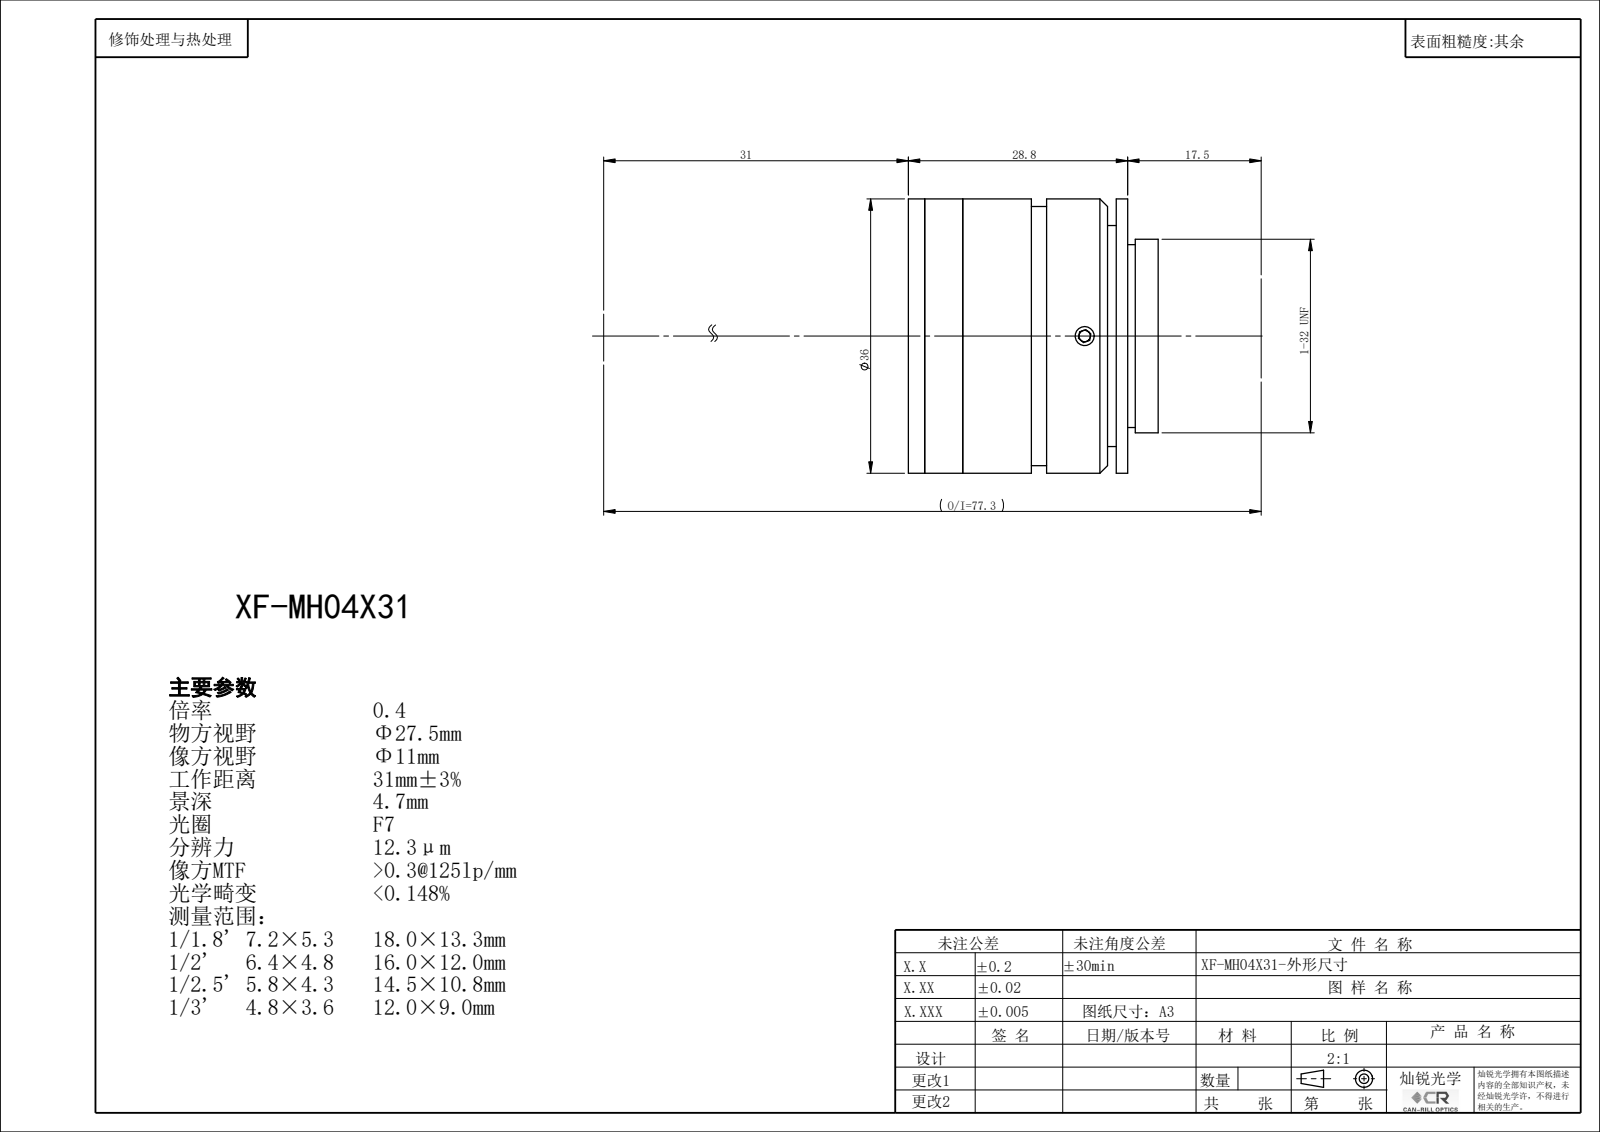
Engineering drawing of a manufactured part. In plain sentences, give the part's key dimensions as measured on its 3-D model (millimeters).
The part is named "XF-MH04X31". Its 3-D file was written by "SolidWorks 2022 (CONFIG_CONTROL_DESIGN)". It is 0 solids with 109 faces: 51 planar, 48 cylindrical and 10 other. Overall it measures 36 by 36 by 32.8 millimeters. Round holes: 3 of diameter 2.5, 1 of diameter 7, 1 of diameter 8.4, 1 of diameter 10, 1 of diameter 12, 1 of diameter 14, 1 of diameter 16, 1 of diameter 18, 1 of diameter 20, 1 of diameter 21.5, 1 of diameter 22, 1 of diameter 24. Round bosses or shafts: 1 of diameter 36, 1 of diameter 34, 1 of diameter 25.4. The main face-to-face distances are 5, 21.65, 7.15, 2.15, 26.65, 28.8, 20.15, 2, 1, 1.5.
